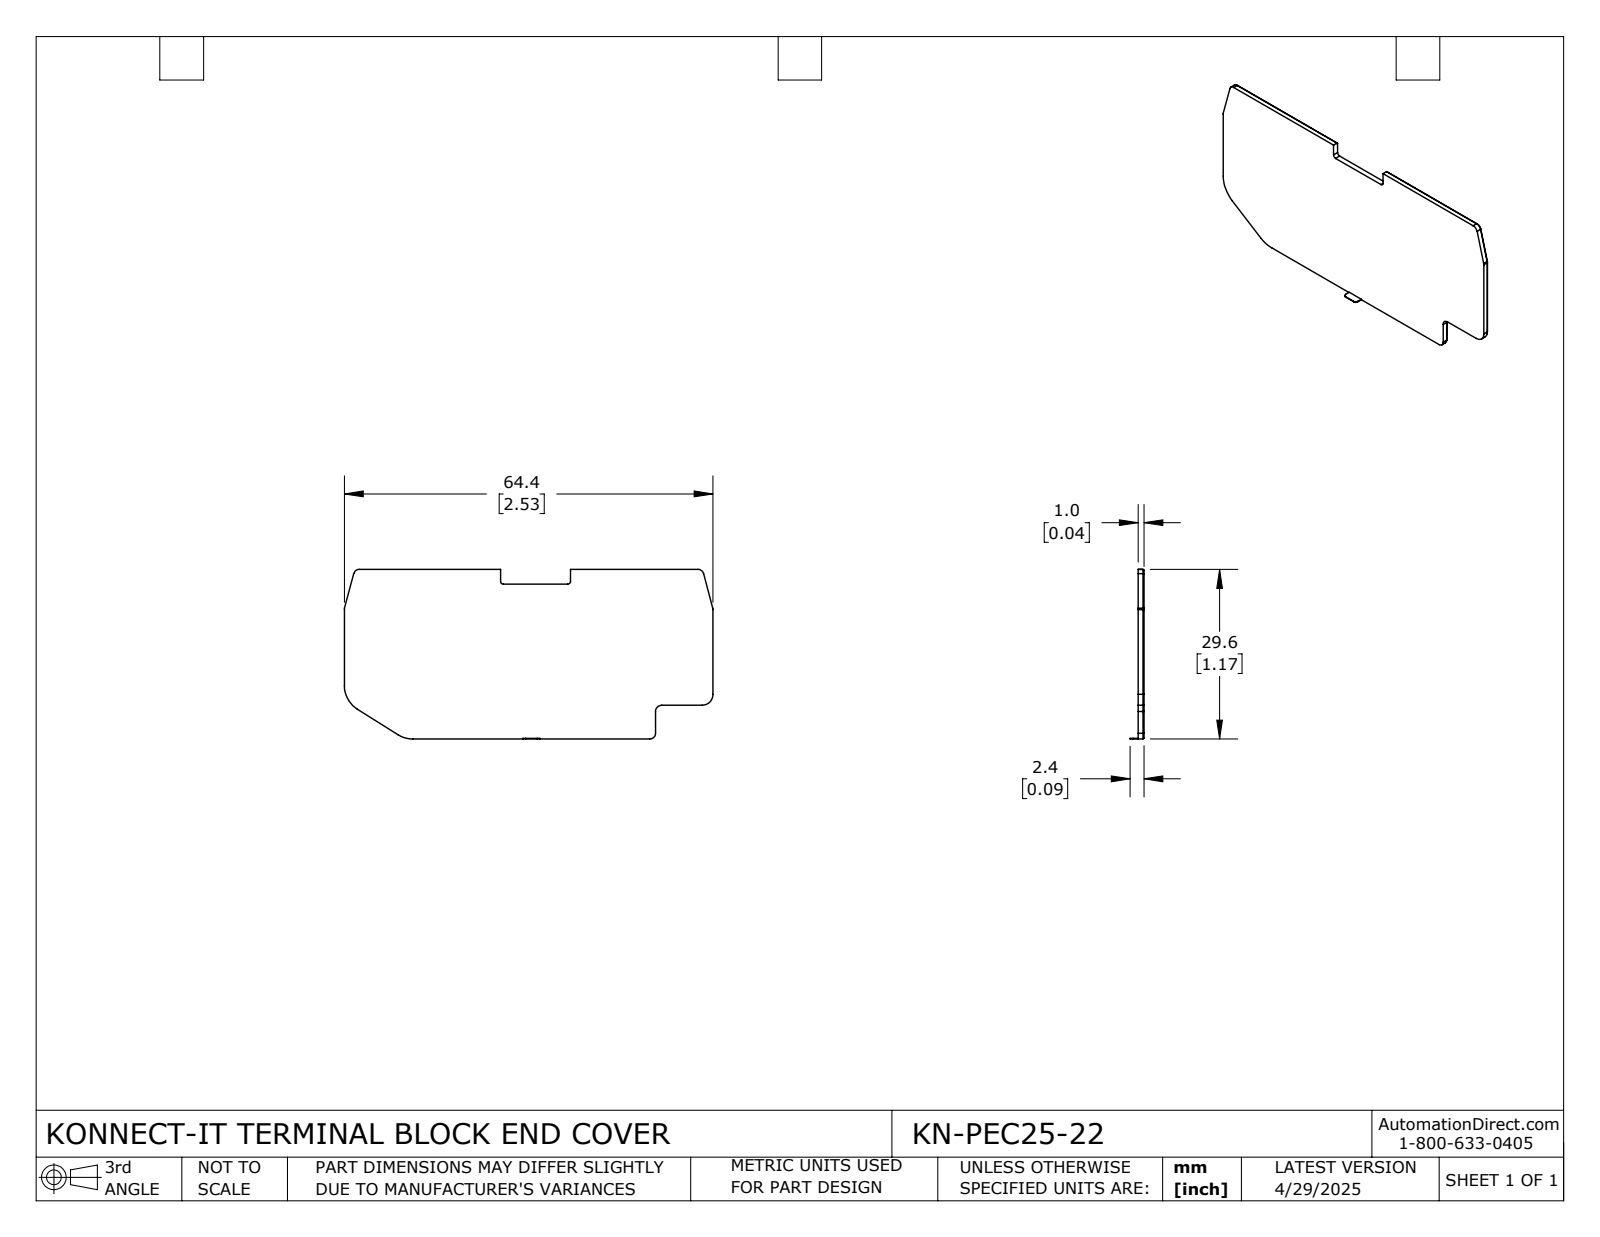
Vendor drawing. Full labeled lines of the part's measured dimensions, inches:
Part name (STEP PRODUCT): KN-PEC25-22
STEP written by: SolidWorks 2024 (CONFIG_CONTROL_DESIGN)
Units: inches
Bodies: 1 solid, 52 faces (30 planar, 22 cylindrical, 0 other)
Overall size (bounding box): 2.534 × 1.166 × 0.094
Volume: 0.108 in³ · Surface area: 5.768 in²
Partial cylindrical surfaces — rounded edges, fillets, slot ends (radius × count): R0.035 ×5, R0.039 ×5, R0.02 ×4, R0.189 ×2, R0.193 ×2, R0.043 ×1, R0.047 ×1, R0.071 ×1
Main face-to-face distances: 0.039, 1.166, 1.162, 0.033, 2.534, 1.064, 0.102, 1.06, 1.158, 0.098
